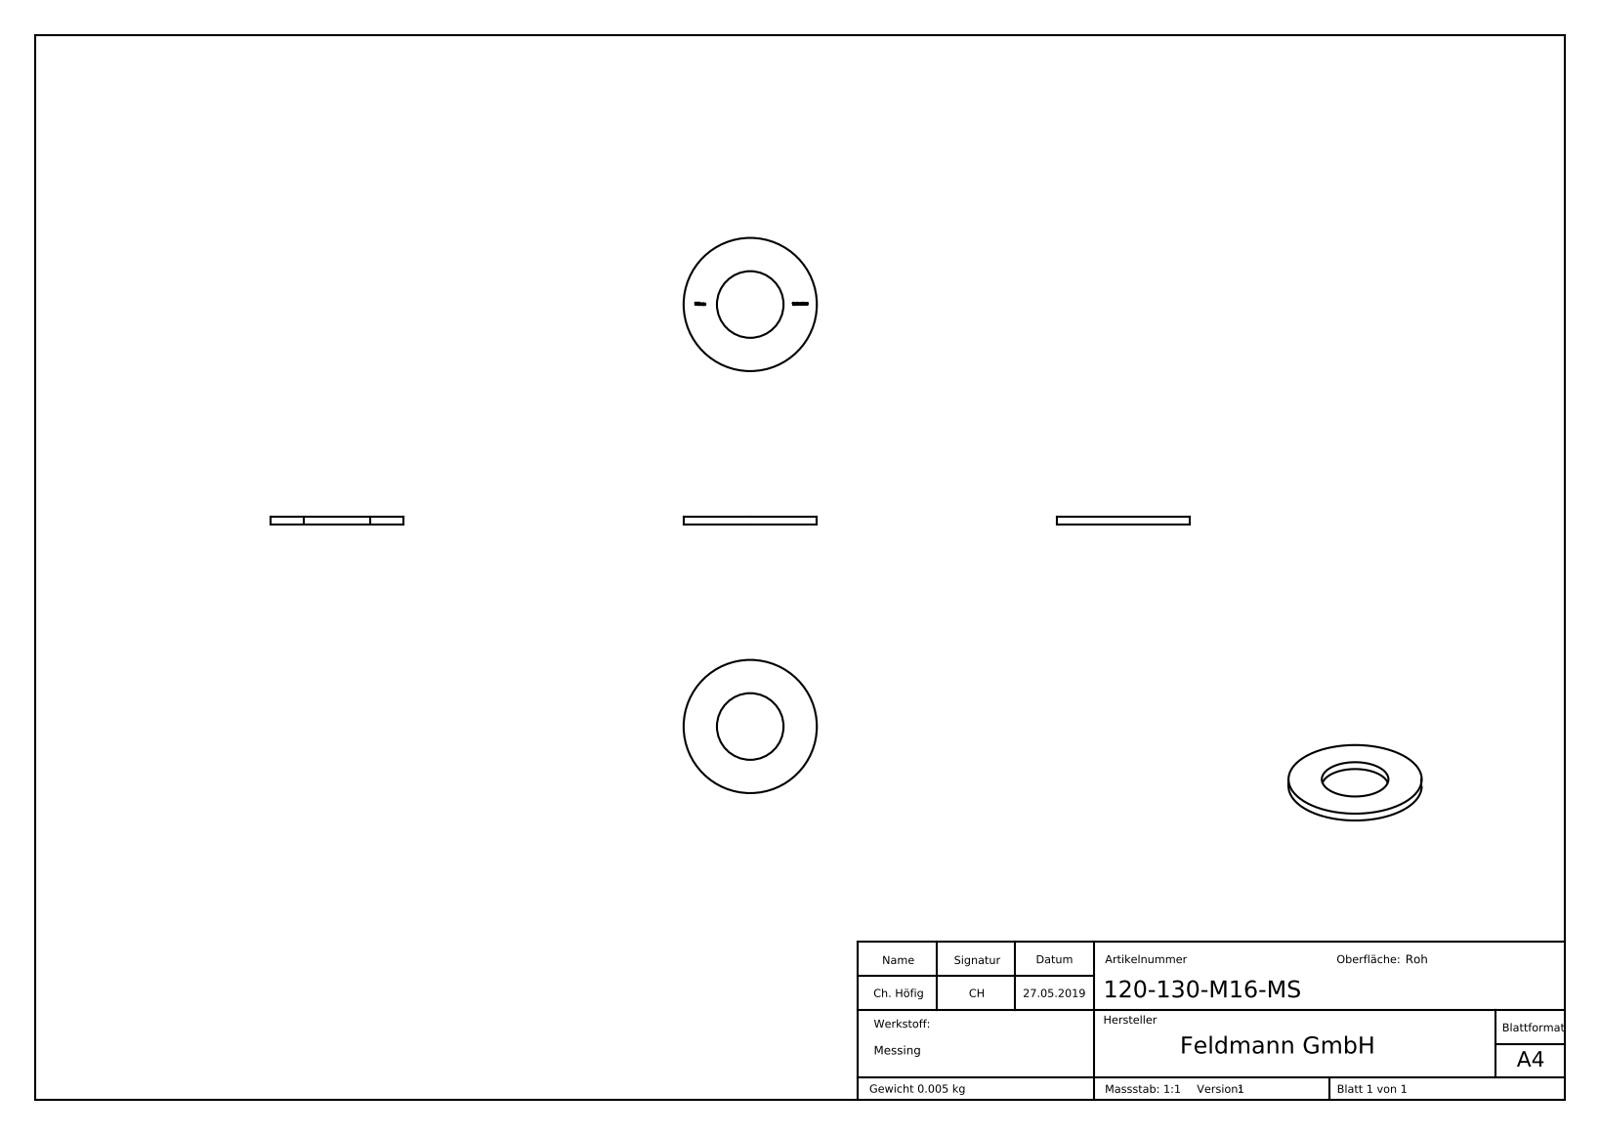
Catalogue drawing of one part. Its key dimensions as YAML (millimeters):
part_name: "120-130-M16-MS"
step_written_by: "SolidWorks 2015 (CONFIG_CONTROL_DESIGN)"
units: millimeters
bodies: {solids: 1, faces: 268, planar: 154, cylindrical: 4, other: 110}
overall_size: [25, 25, 1.5]
volume: 552
surface_area: 915
round_holes:
  - {diameter: 12.5, count: 1}
round_bosses_or_shafts:
  - {diameter: 25, count: 1}
face_to_face_distances: [1.5, 1.4, 0.86, 0.77, 0.73, 0.84, 17.87, 18.6, 19.67, 1.8]
